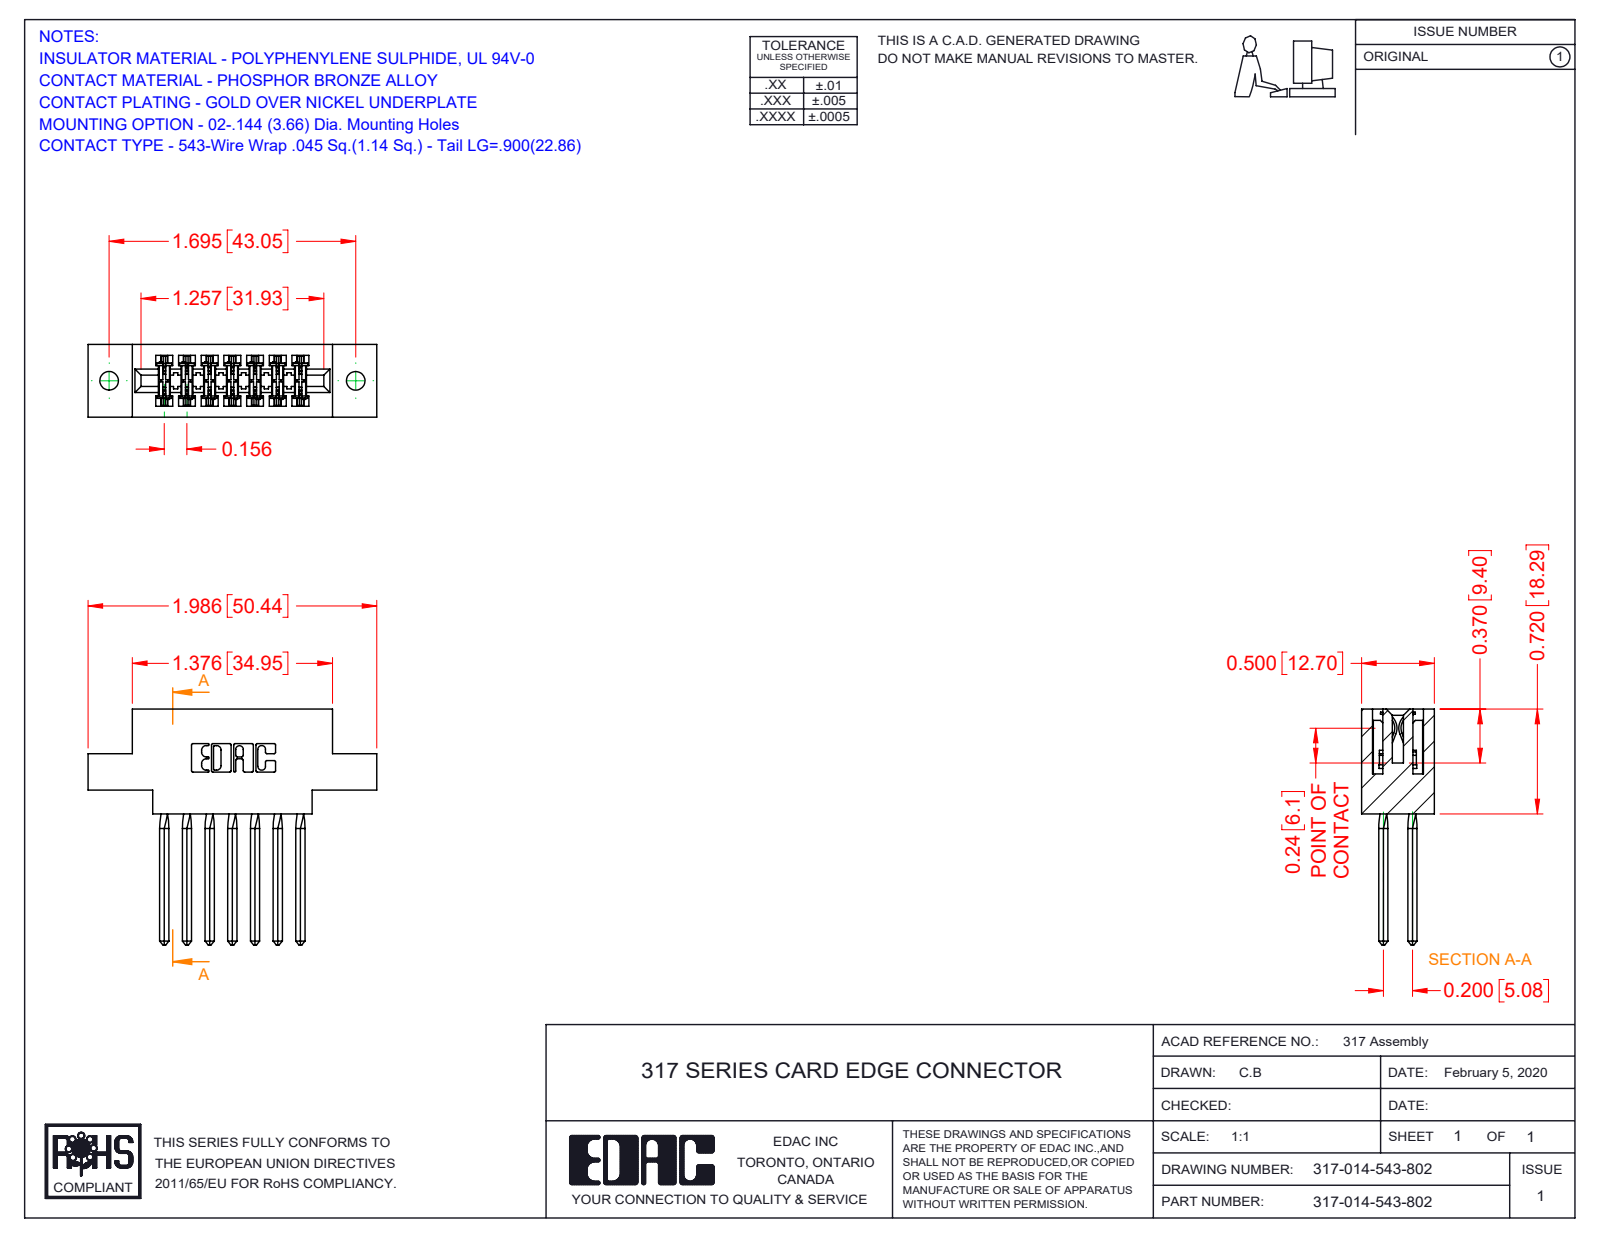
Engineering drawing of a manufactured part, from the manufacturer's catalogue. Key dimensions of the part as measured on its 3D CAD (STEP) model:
Part name (STEP PRODUCT): 317 Part_.144 Dia; 317-290-001_543; 317-014-543-802
STEP written by: SolidWorks 2016 (CONFIG_CONTROL_DESIGN)
Units: inches
Bodies: 15 solids, 1348 faces (1080 planar, 212 cylindrical, 56 other)
Overall size (bounding box): 1.986 × 1.62 × 0.5
Volume: 0.446 in³ · Surface area: 14.67 in²
Round holes (diameter × count): ⌀0.128 ×2
Partial cylindrical surfaces — rounded edges, fillets, slot ends (radius × count): R0.015 ×28, R0.01 ×22, R0.007 ×6, R0.031 ×6, R0.026 ×3, R0.095 ×2, R0.1 ×2, R0.11 ×2
Main face-to-face distances: 0.11, 0.5, 0.075, 0.425, 0.22, 0.156, 0.116, 0.065, 0.331, 0.163
Hole centre spacings: 1.695
